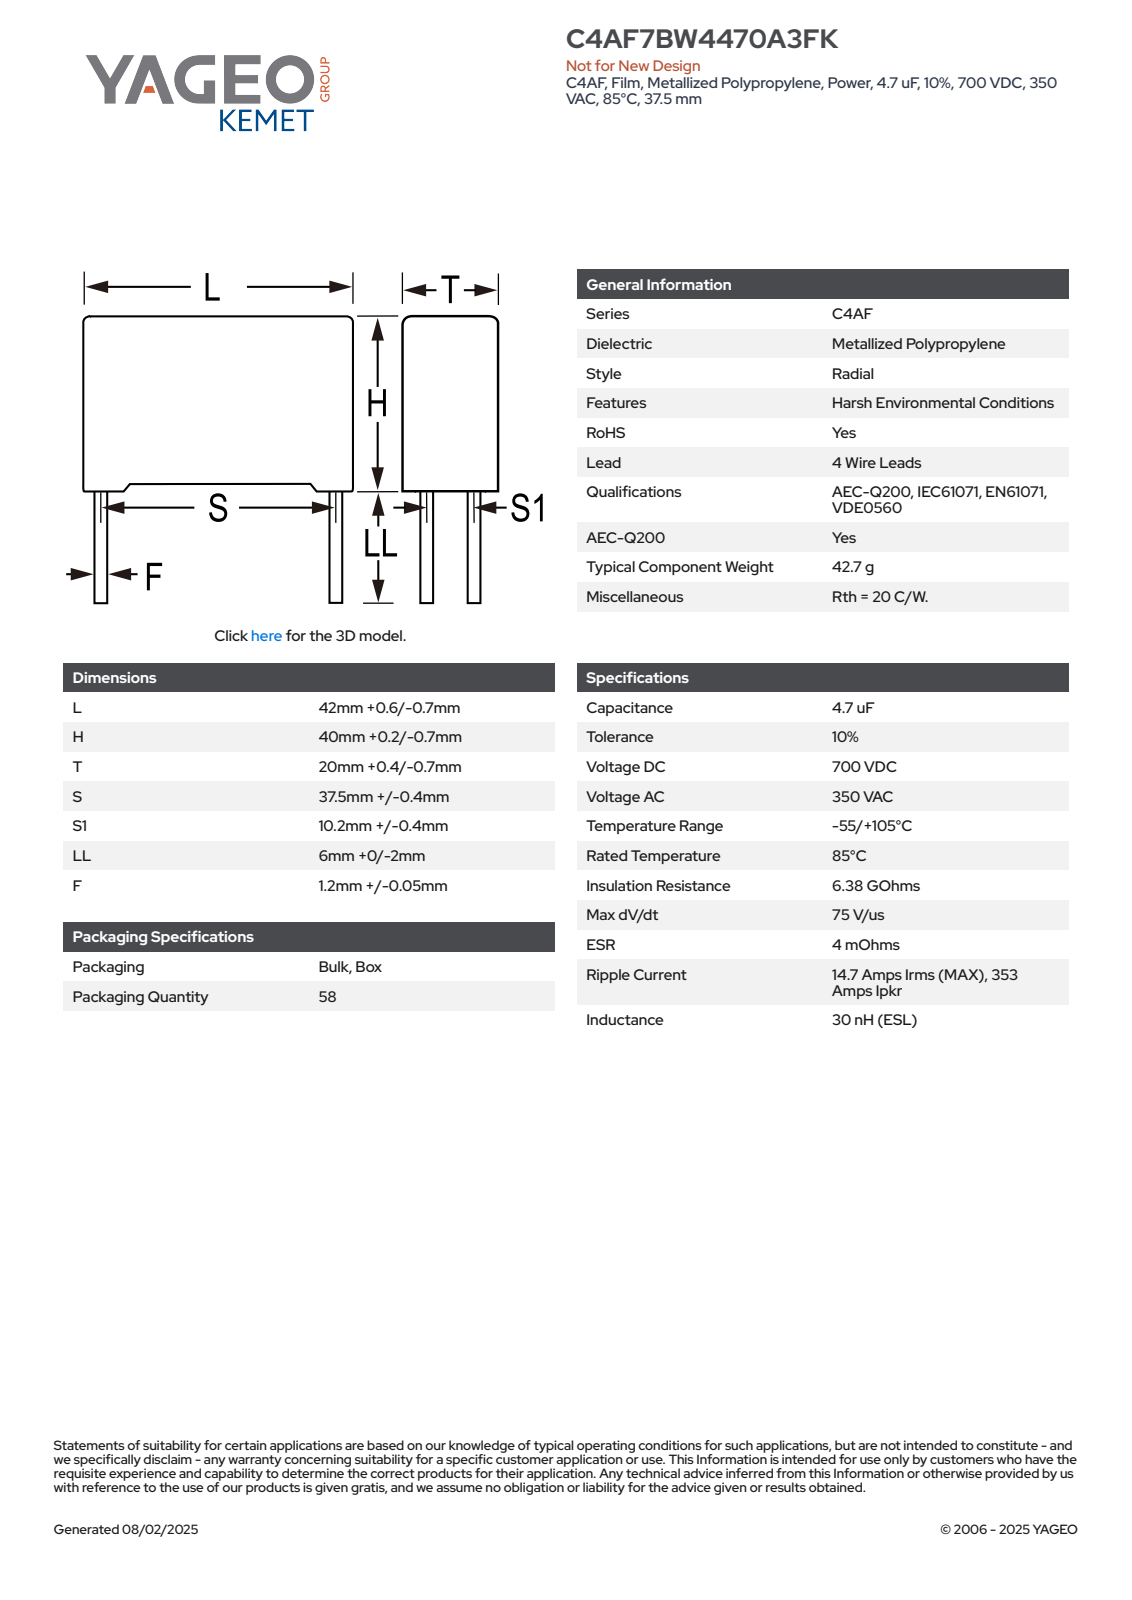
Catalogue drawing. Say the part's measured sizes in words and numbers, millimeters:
The part is named "CFP_RB4_42X40X20_L42.6H40.2T20.4S37.5S110.2LL6F1.25". Its 3-D file was written by "SolidWorks 2014 (AUTOMOTIVE_DESIGN)". It is 4 solids with 87 faces: 79 planar, 8 cylindrical and 0 other. Overall it measures 46.2 by 42.6 by 20.41 millimeters. Its volume is 34 041 cubic millimeters and its surface area 7 042 square millimeters. Round bosses or shafts: 4 of diameter 1.25. The main face-to-face distances are 20.4, 42.6, 39.02, 1.18, 40.2, 1.25, 20.41, 41.35, 19.15, 40.1.
